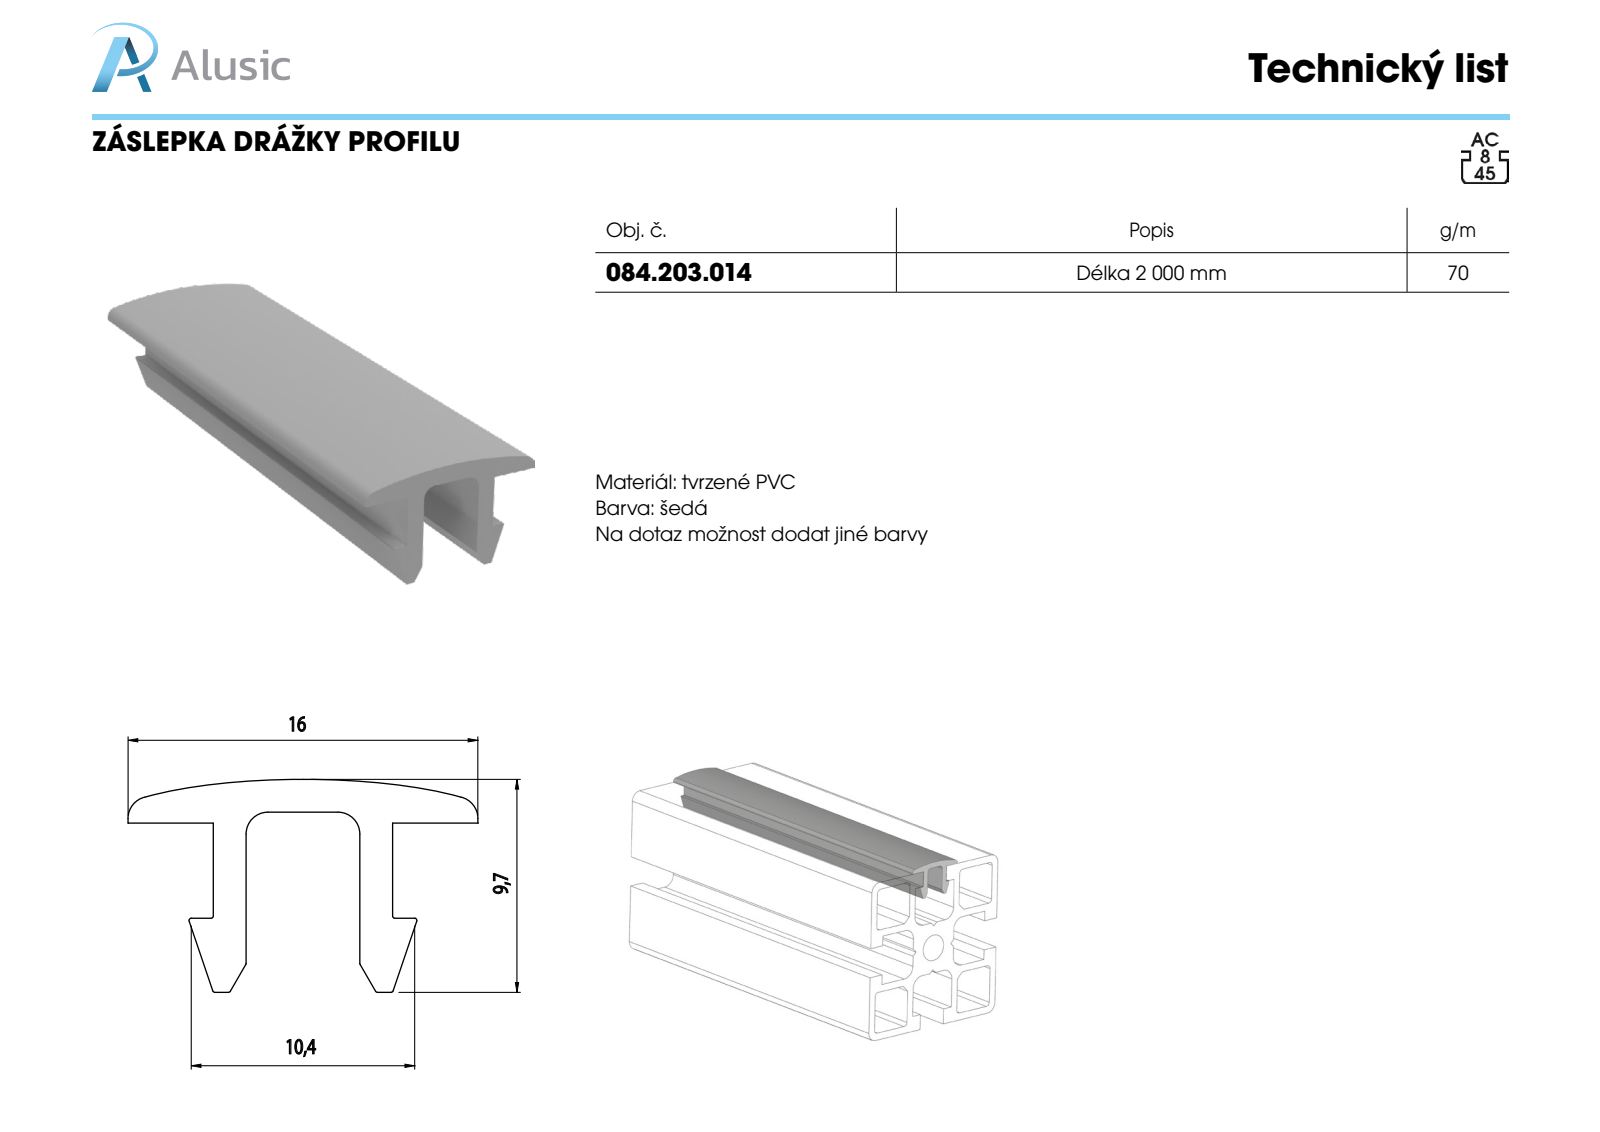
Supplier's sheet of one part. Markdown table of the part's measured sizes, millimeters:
| quantity | value |
| --- | --- |
| part name | 084.203.014 |
| STEP written by | SolidWorks 2011 (CONFIG_CONTROL_DESIGN) |
| units | millimeters |
| bodies | 1 solid, 35 faces (19 planar, 16 cylindrical, 0 other) |
| overall size | 100 × 16 × 9.74 |
| volume | 5 042 mm³ |
| surface area | 6 705 mm² |
| partial cylindrical surfaces (radius × count) | 0.1 × 10, 1 × 4, 32.51 × 1 |
| main face-to-face distances | 1.5, 6.71, 5.21, 8.21, 0.5, 4.35, 4.85, 3.39, 7.74, 8.24 |
